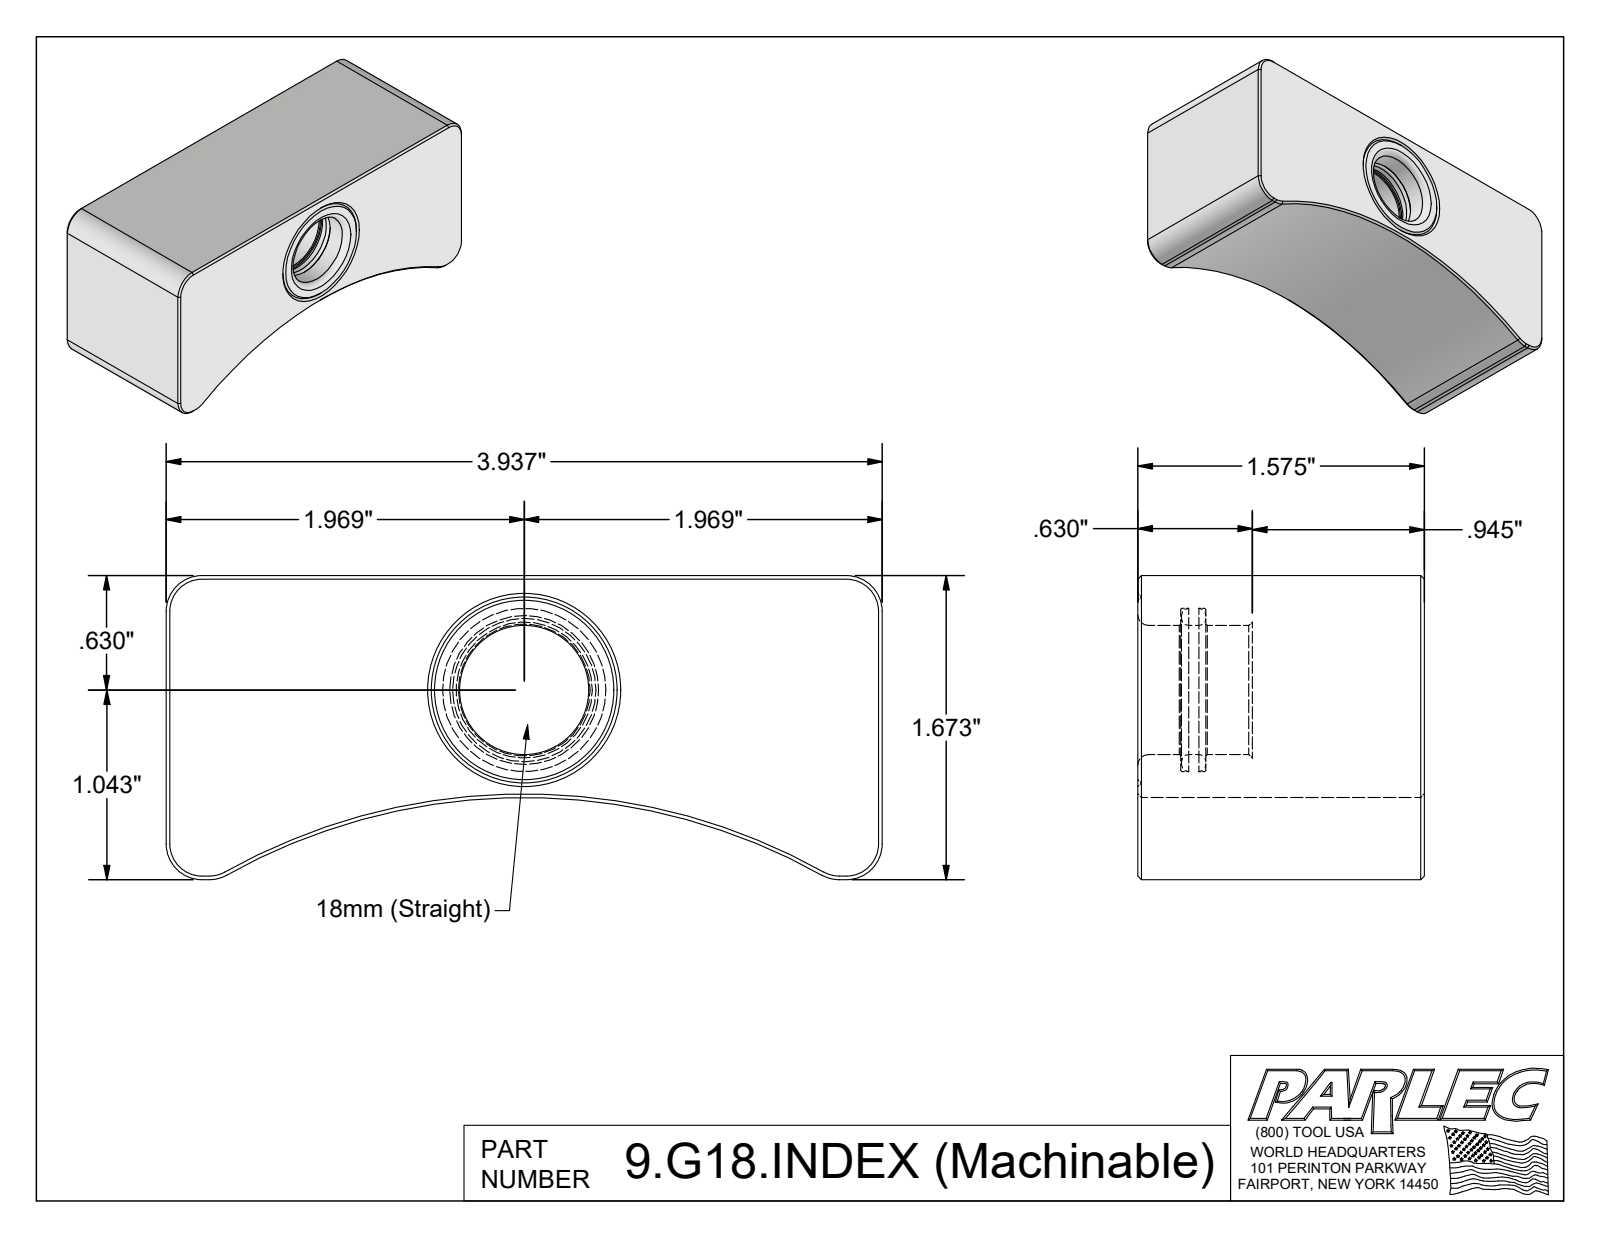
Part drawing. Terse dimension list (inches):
name: 9.G18.INDEX (Machinable)
written by: Autodesk Inventor 2022 (AUTOMOTIVE_DESIGN)
unit: in
bodies: 1 solid, 61 faces (23 planar, 12 cylindrical, 26 other)
size: 3.937 × 1.673 × 1.575
volume: 8.44 in³; area: 30.75 in²
holes: 1× ⌀0.709, 1× ⌀0.898
rounds: 6× R0.197, 1× R3.346
face distances: 1.575, 3.937, 0.945, 0.63, 1.339, 0.394, 0.236, 1.201, 0.256, 0.138
